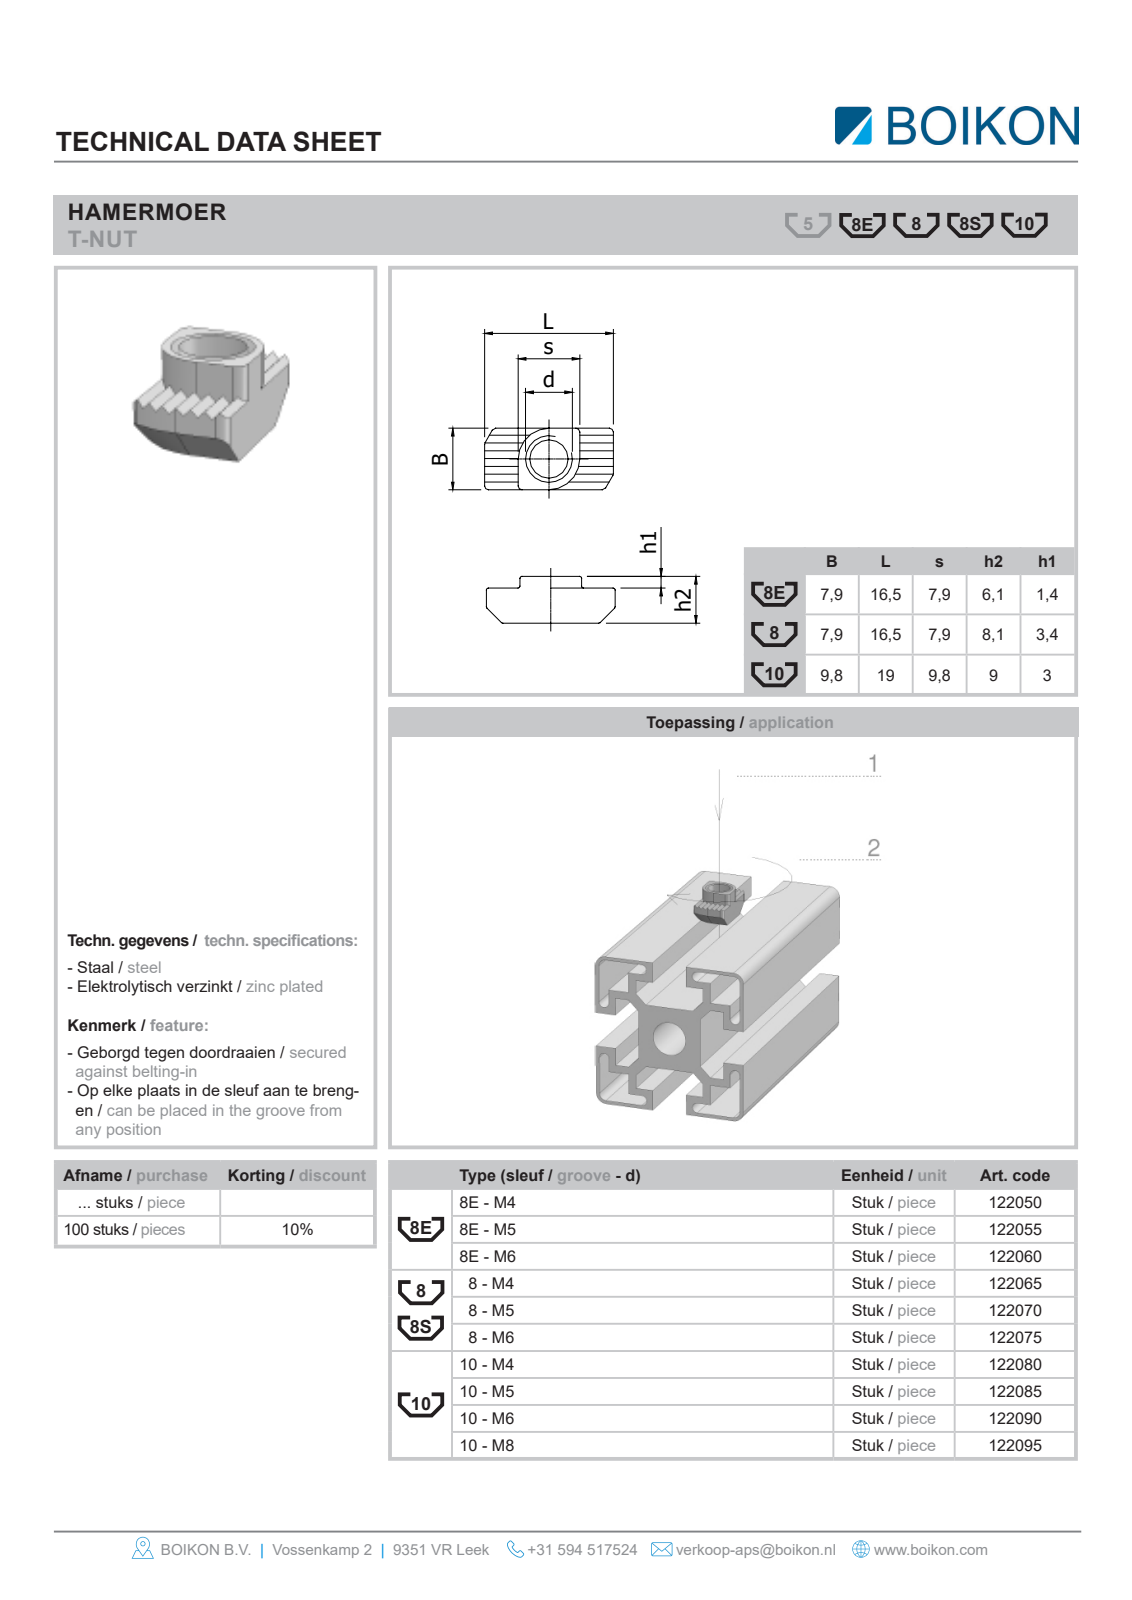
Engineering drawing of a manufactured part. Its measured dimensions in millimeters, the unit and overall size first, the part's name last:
Units: millimetres
Overall size (bounding box): 19 × 11.8 × 9.7
Round holes (diameter × count): ⌀3.14 ×1
Partial cylindrical surfaces — rounded edges, fillets, slot ends (radius × count): R1 ×5, R5 ×2, R1.16 ×1, R9.5 ×1
Main face-to-face distances: 0.99, 9.7, 1.98, 8.8, 2.97, 3.96, 4.95, 5.94, 4.65, 14.35
Volume: 1 081 mm³ · Surface area: 812 mm²
Bodies: 1 solid, 51 faces (38 planar, 11 cylindrical, 2 other)
Part name (STEP PRODUCT): Root; 122080 Hamermoer 10 - M4BOIKON
STEP written by: HiCAD 2013 1802.4 Build 509 (AUTOMOTIVE_DESIGN)
